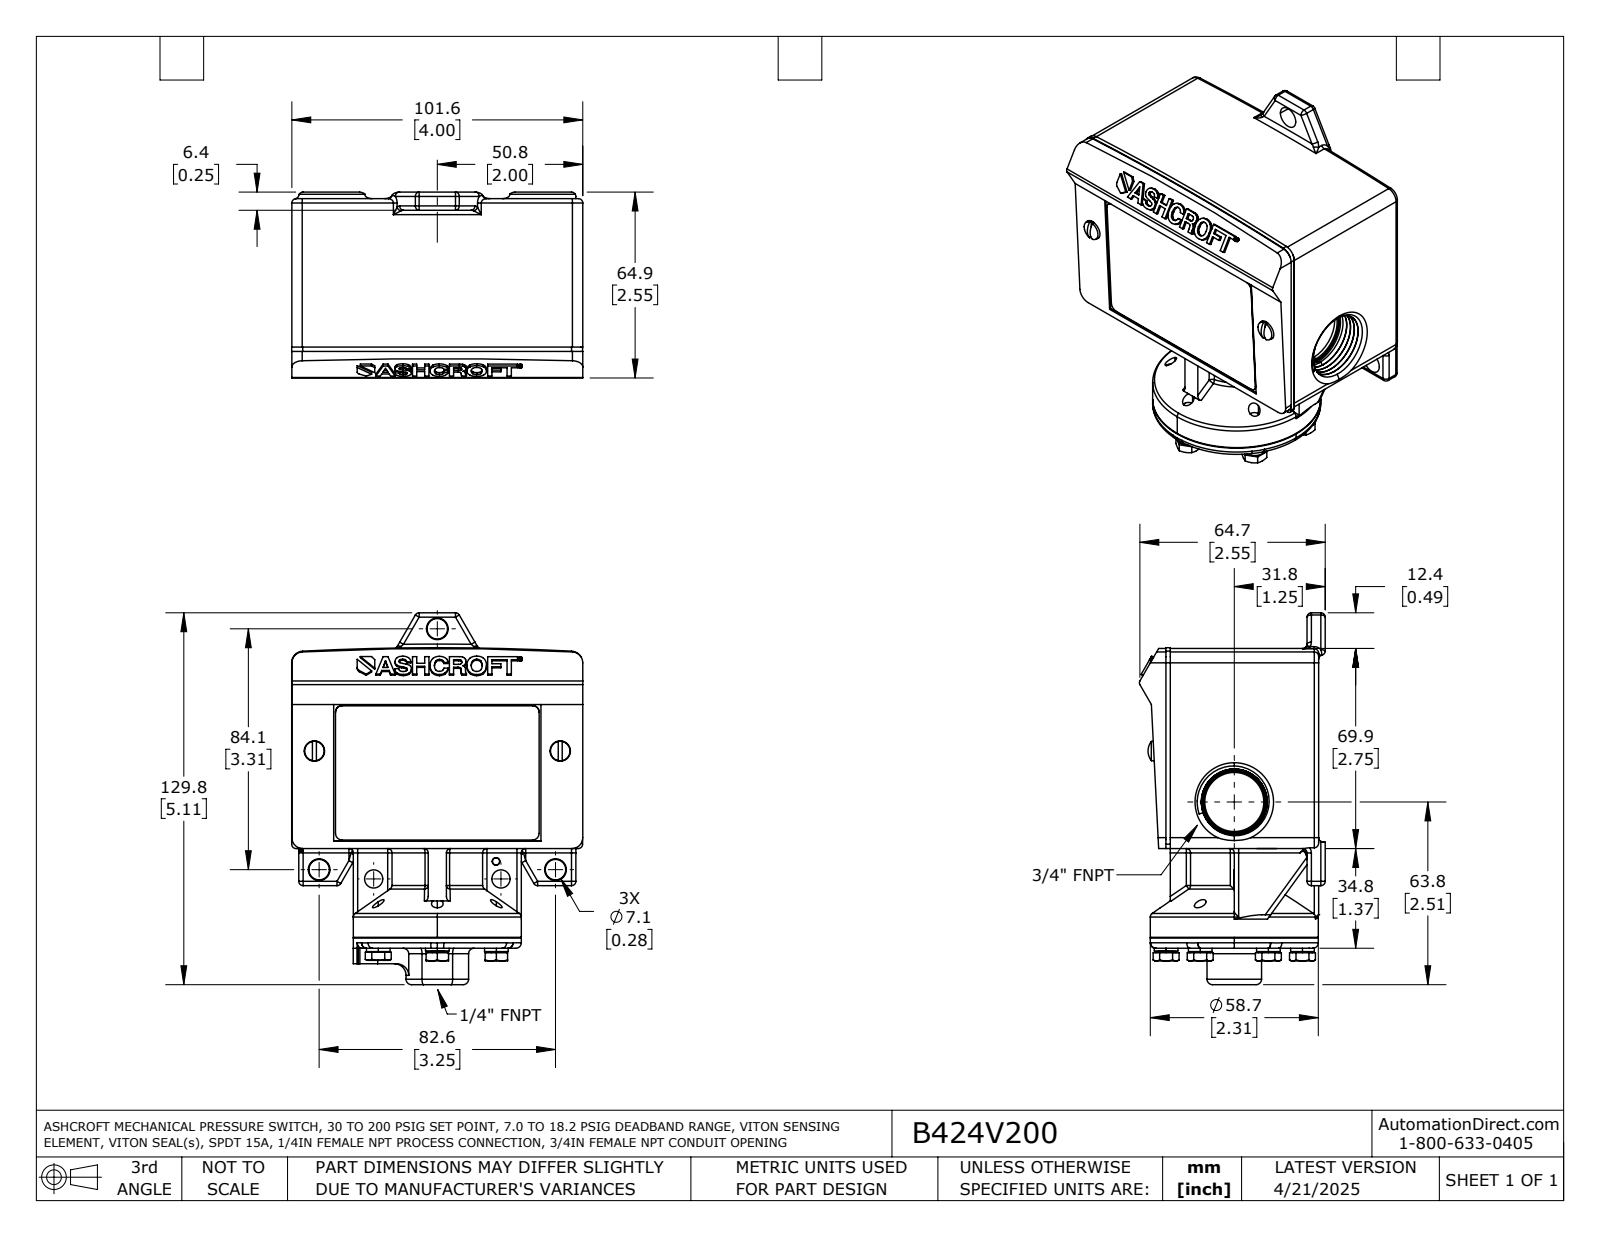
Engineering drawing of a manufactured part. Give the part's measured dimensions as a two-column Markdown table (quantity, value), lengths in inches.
| quantity | value |
| --- | --- |
| part name | B424V200 |
| STEP written by | SolidWorks 2021 (AUTOMOTIVE_DESIGN) |
| units | inches |
| bodies | 2 solids, 1259 faces (345 planar, 472 cylindrical, 442 other) |
| overall size | 5.111 × 4.003 × 2.555 |
| volume | 28.57 in³ |
| surface area | 84.51 in² |
| round holes (diameter × count) | 0.161 × 6, 0.192 × 5, 0.209 × 5, 0.187 × 4, 0.28 × 2, 0.455 × 1, 0.812 × 1 |
| round bosses / shafts (diameter × count) | 0.325 × 6, 0.278 × 6, 0.19 × 5, 0.27 × 2, 0.25 × 2, 2.31 × 1 |
| partial cylindrical surfaces (radius × count) | 0.06 × 92, 0.03 × 5, 0.075 × 4, 0.09 × 4, 0.15 × 4, 0.01 × 2, 0.094 × 2, 0.16 × 2 |
| main face-to-face distances | 4, 0.015, 1.37, 0.09, 3.91, 0.44, 3.56, 3.47, 0.35, 0.845 |
| hole center spacings | 0.937, 1.624, 1.875, 0.938, 3.38 |
